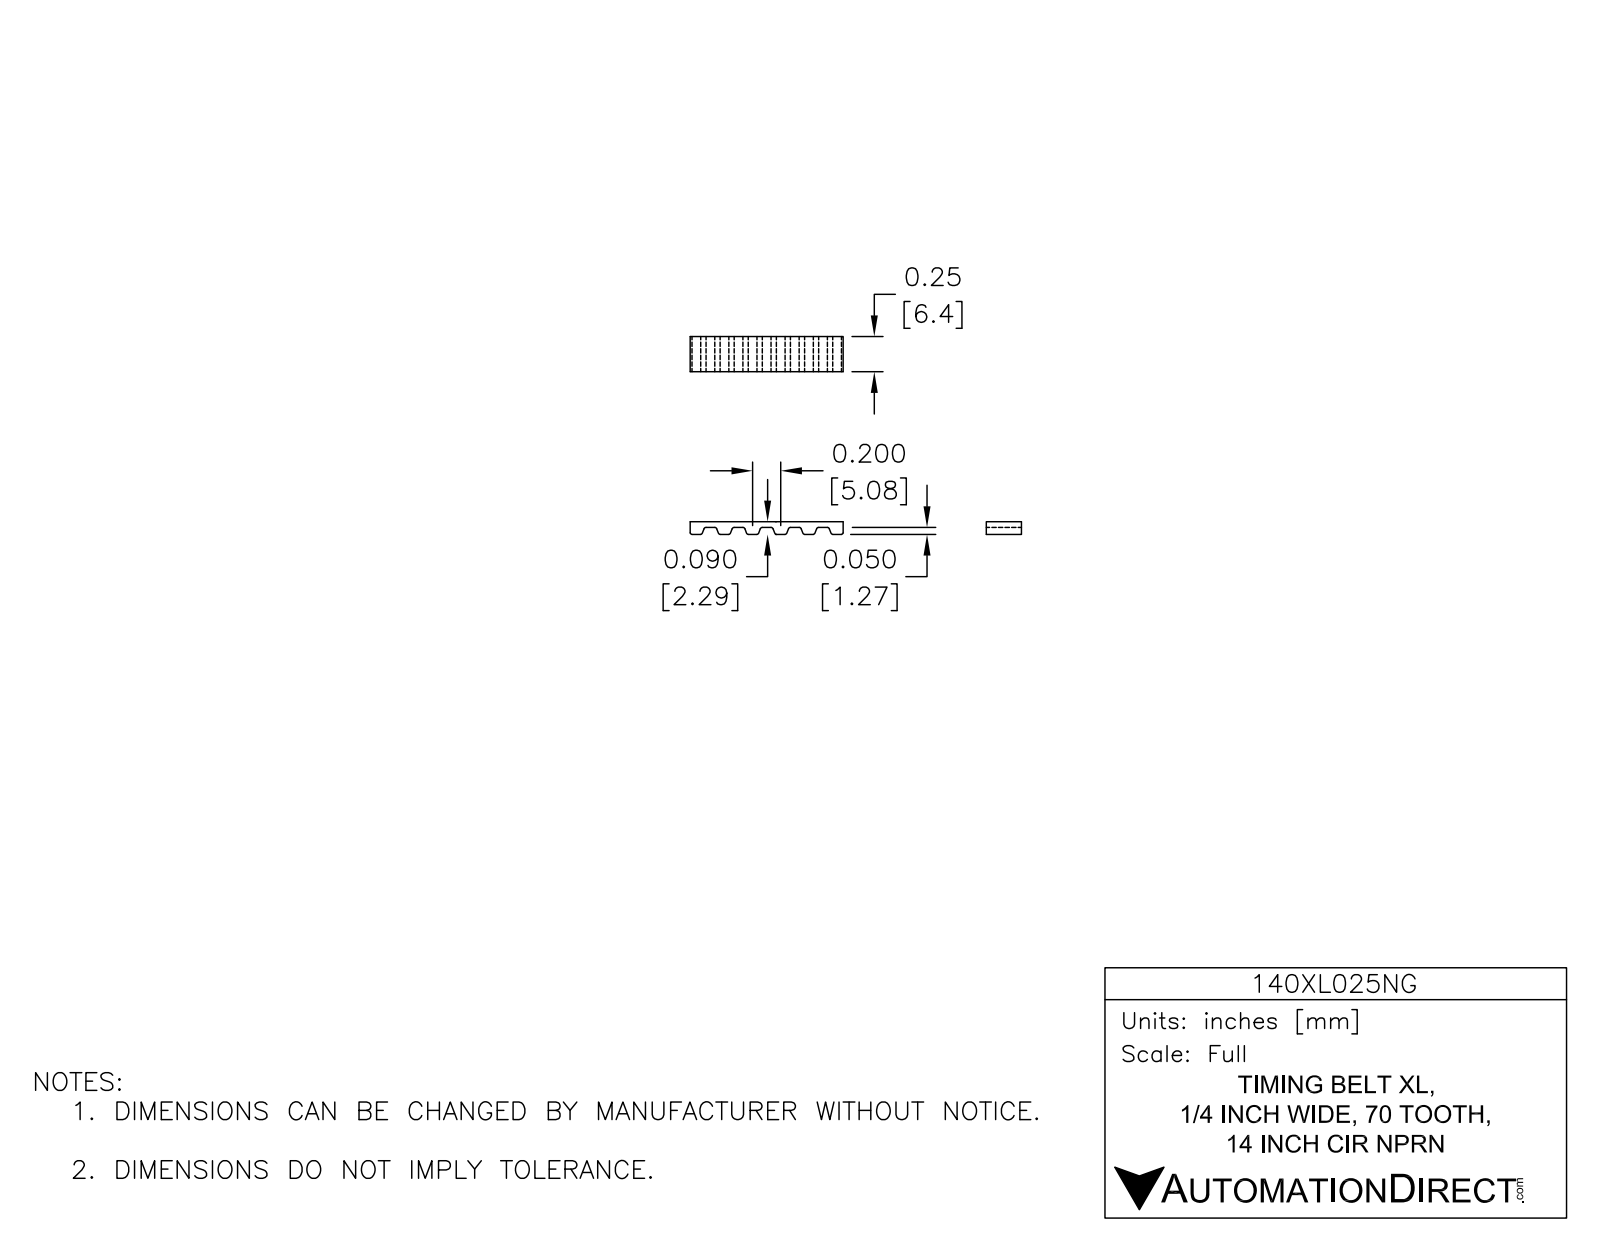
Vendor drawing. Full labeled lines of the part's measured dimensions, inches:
Part name (STEP PRODUCT): 140XL025NG
STEP written by: SolidWorks 2014 (AUTOMOTIVE_DESIGN)
Units: inches
Bodies: 1 solid, 598 faces (238 planar, 360 cylindrical, 0 other)
Overall size (bounding box): 5.288 × 3 × 0.25
Volume: 0.19 in³ · Surface area: 9.421 in²
Partial cylindrical surfaces — rounded edges, fillets, slot ends (radius × count): R0.015 ×280, R1.46 ×2, R1.5 ×2
Main face-to-face distances: 0.25, 0.04, 2.96, 3, 0.178, 2.92, 0.356, 0.534, 0.712, 0.89
